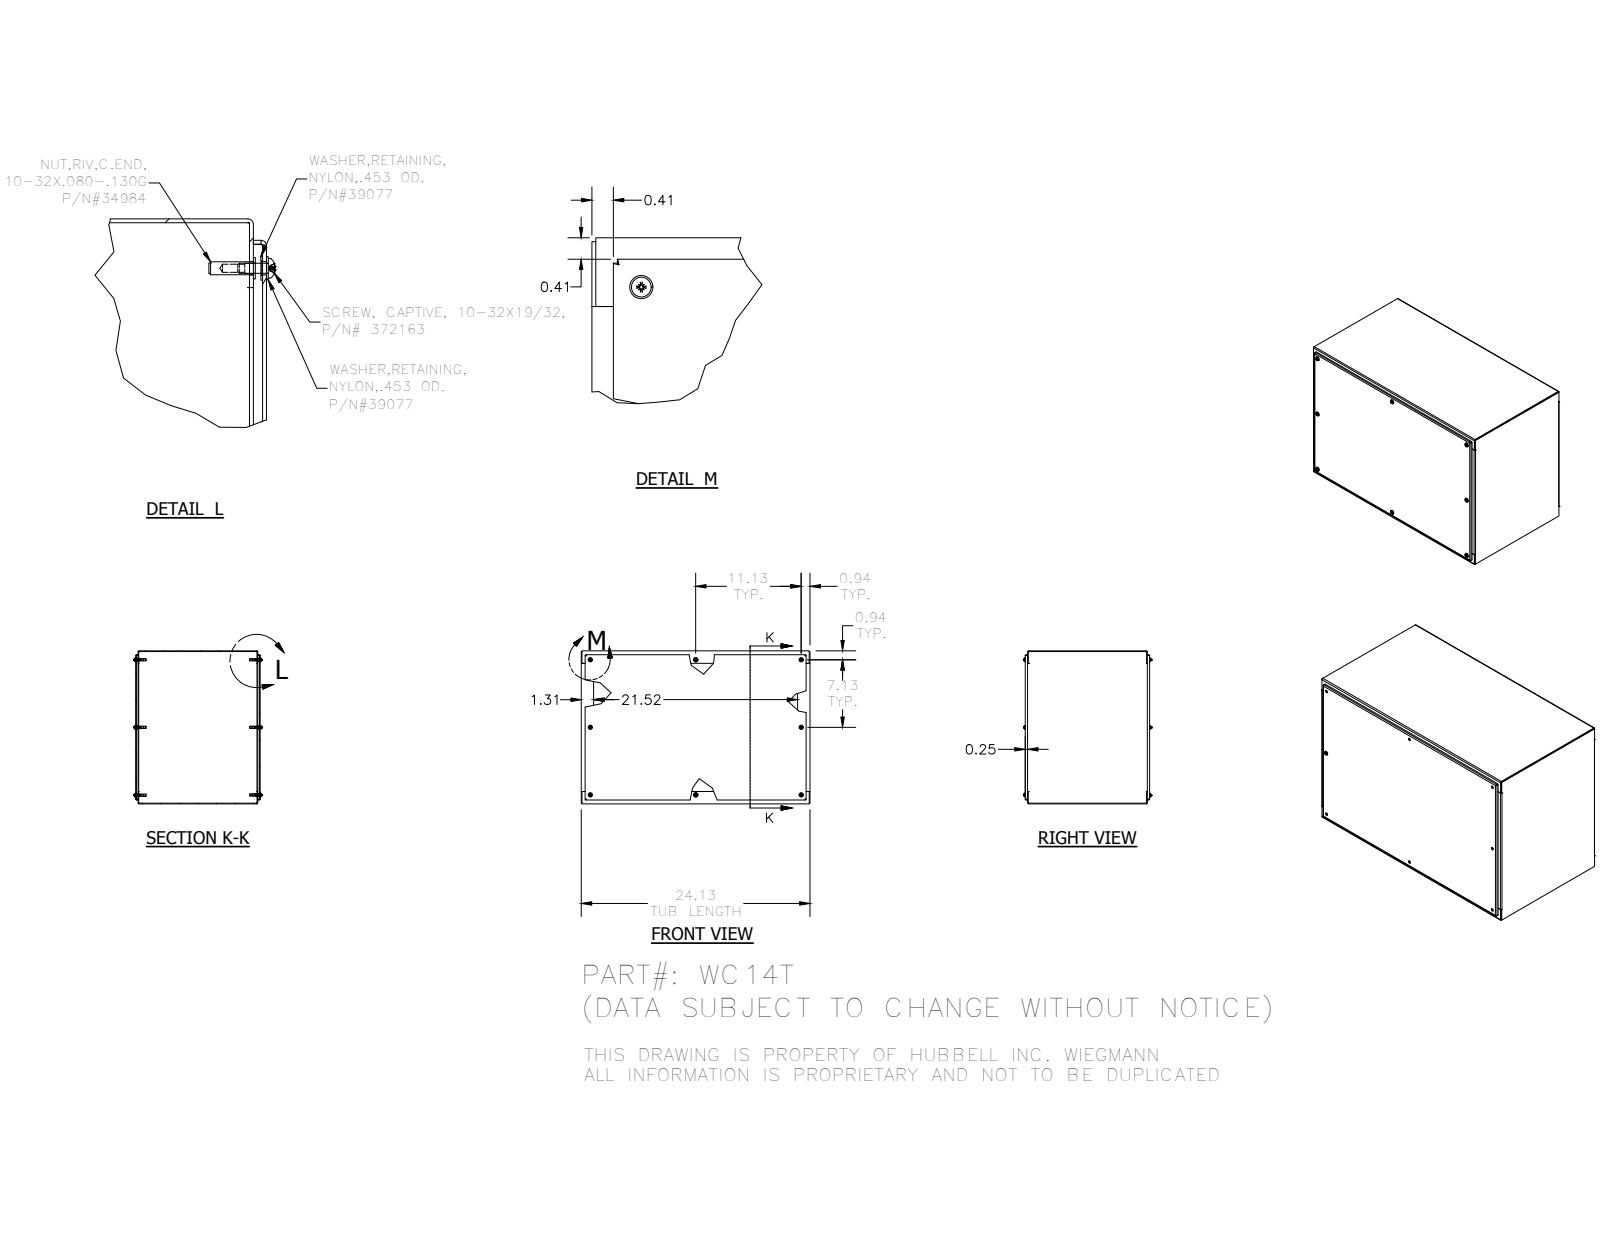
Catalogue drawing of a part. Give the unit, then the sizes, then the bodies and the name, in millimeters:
Units: millimetres
Overall size (bounding box): 612.77 × 409.57 × 341.65
Round holes (diameter × count): ⌀4.78 ×14, ⌀7.06 ×14, ⌀3.96 ×13, ⌀4.98 ×13, ⌀6.35 ×11, ⌀6.53 ×8
Round bosses / shafts (diameter × count): ⌀11.51 ×14, ⌀11.11 ×14, ⌀9.47 ×14, ⌀4.83 ×14, ⌀10.31 ×13, ⌀6.3 ×13
Partial cylindrical surfaces — rounded edges, fillets, slot ends (radius × count): R0.79 ×16, R2.67 ×16, R2.27 ×14
Main face-to-face distances: 1.88, 331.5, 407.7, 610.9, 6.35, 325.15, 329.62, 333.38, 405.82, 409.58
Hole centre spacings: 565.15, 282.57, 459.19, 282.58, 361.95, 593.42, 283.33, 361.96
Volume: 2 349 000 mm³ · Surface area: 2 531 000 mm²
Bodies: 71 solids, 1422 faces (760 planar, 292 cylindrical, 370 other)
Part name (STEP PRODUCT): 34984; WC14TLRS; WC14TTB; 39035 (+4 more)
STEP written by: Autodesk Inventor 2016 (AUTOMOTIVE_DESIGN)
